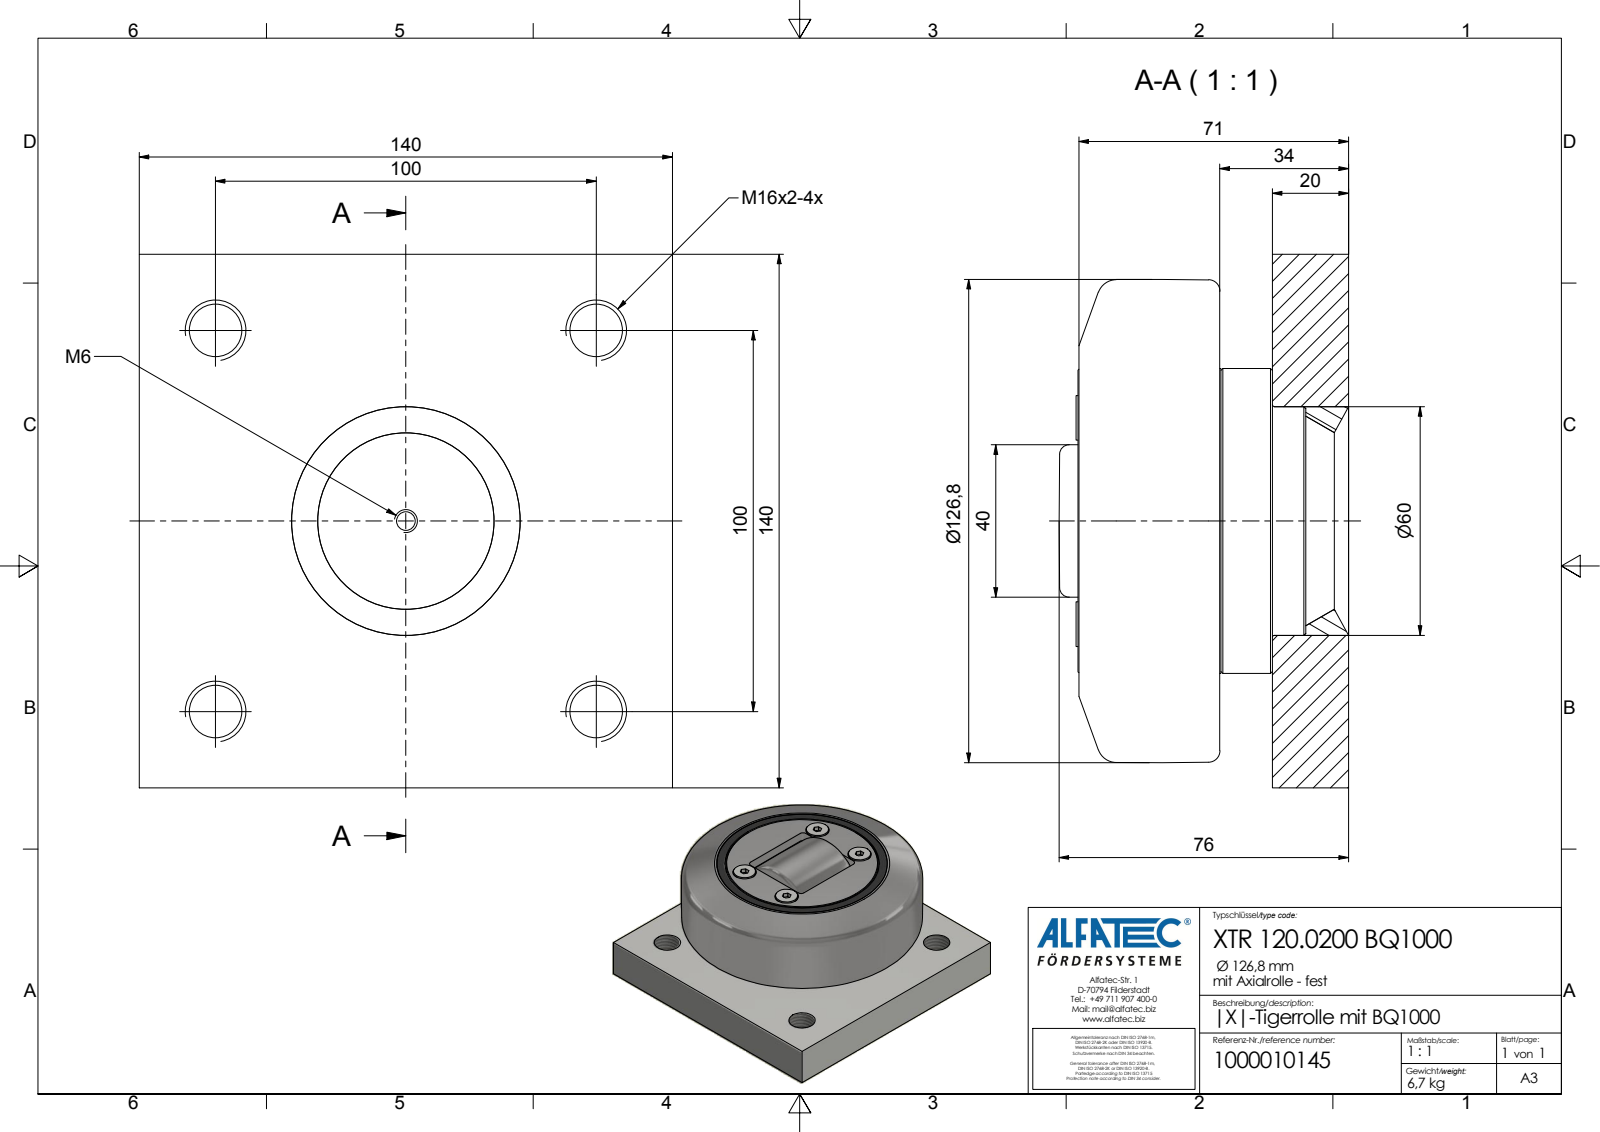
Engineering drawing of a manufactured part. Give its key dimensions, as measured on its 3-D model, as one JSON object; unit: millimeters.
{"part_name": "XTR 120.0200 BQ1000_Kontur", "step_written_by": "Autodesk Inventor 2020 (AUTOMOTIVE_DESIGN)", "units": "millimeters", "bodies": {"solids": 3, "faces": 143, "planar": 68, "cylindrical": 48, "other": 27}, "overall_size": [140, 140, 76], "volume_mm3": 801457, "surface_area_mm2": 132238, "round_holes": [[3, 4], [13.84, 4], [4.92, 1], [22.3, 1], [29.3, 1], [33.5, 1], [71, 1], [81, 1], [87, 1], [89.5, 1], [95, 1]], "round_bosses_or_shafts": [[11.7, 4], [84.5, 1], [80, 1], [79.8, 1], [79, 1], [69.5, 1]], "partial_cylinders_radius": [[2, 8], [1.5, 2], [24.5, 1]], "face_to_face_distances": [20, 140, 33.8, 13.8, 6.5, 71, 51, 37.2, 30.5, 30.7], "hole_center_spacings": [70.71, 100, 141.42]}
